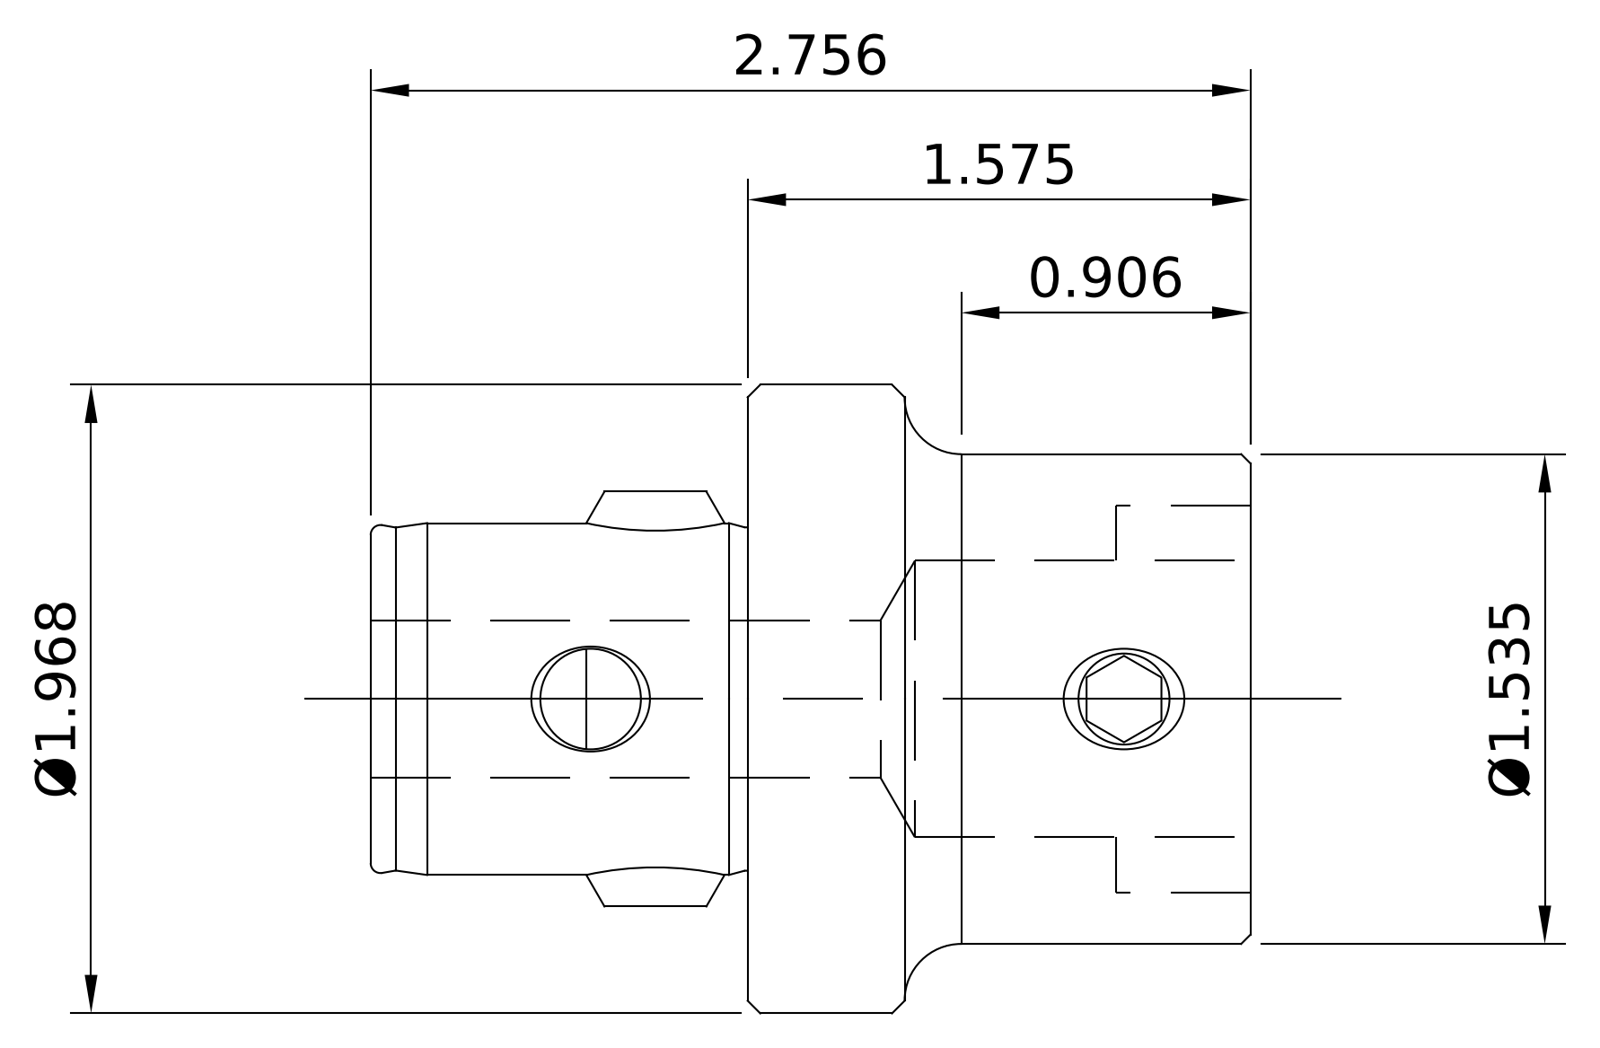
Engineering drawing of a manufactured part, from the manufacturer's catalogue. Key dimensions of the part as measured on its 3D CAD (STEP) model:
Part name (STEP PRODUCT): 11.332.541; 10.690.43X_10.690.434; 10.691.50X_10.691.505; 691-50XRing_10.691.505Ring (+1 more)
STEP written by: SolidWorks 2015 (CONFIG_CONTROL_DESIGN)
Units: millimetres
Bodies: 4 solids, 148 faces (41 planar, 49 cylindrical, 58 other)
Overall size (bounding box): 70 × 50 × 50
Volume: 60 223 mm³ · Surface area: 17 166 mm²
Round holes (diameter × count): ⌀4.5 ×1, ⌀6.8 ×1, ⌀8 ×1, ⌀8.2 ×1, ⌀11 ×1, ⌀12 ×1, ⌀12.5 ×1, ⌀14.5 ×1, ⌀22 ×1, ⌀22.5 ×1
Round bosses / shafts (diameter × count): ⌀50 ×1, ⌀39 ×1, ⌀38.6 ×1, ⌀28 ×1, ⌀10.9 ×1, ⌀8.8 ×1, ⌀8 ×1, ⌀6.9 ×1
Partial cylindrical surfaces — rounded edges, fillets, slot ends (radius × count): R3.5 ×2, R14 ×1
Main face-to-face distances: 40, 30, 70, 18.91, 4, 11, 59.4, 29.4, 10.6, 22
Hole centre spacings: 15, 42.45
